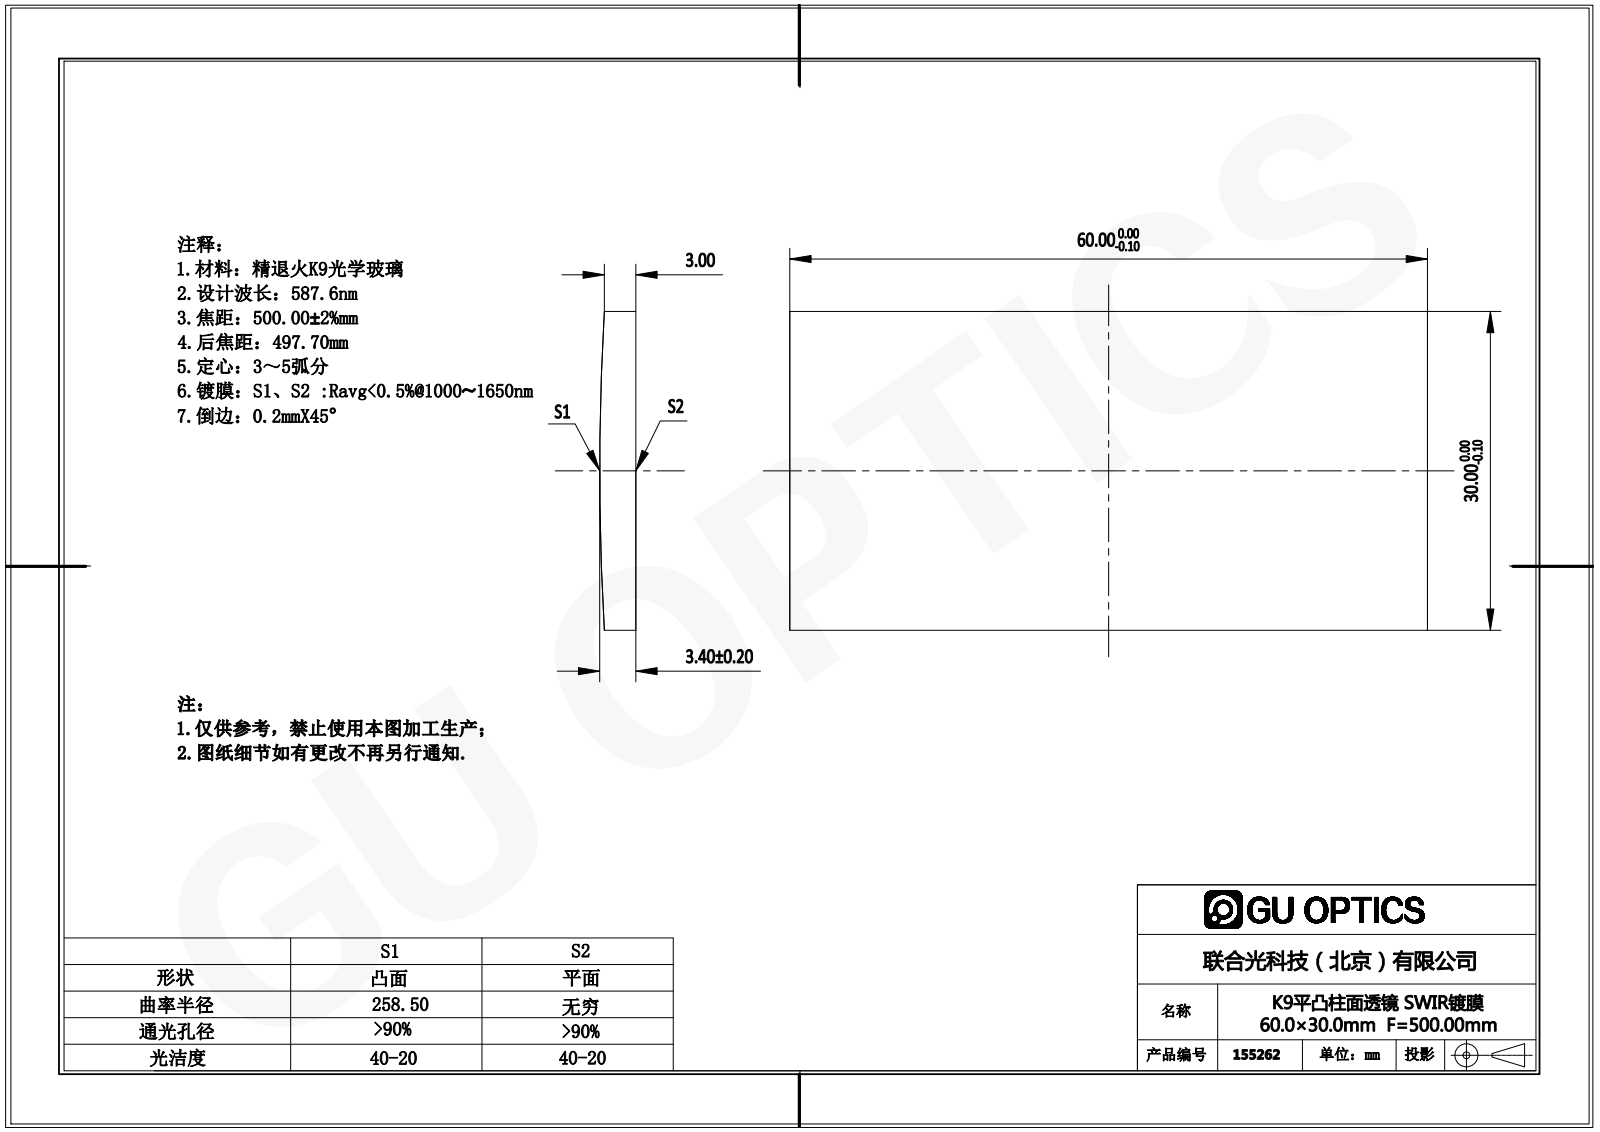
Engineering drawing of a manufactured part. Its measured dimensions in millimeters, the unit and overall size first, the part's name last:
Units: millimetres
Overall size (bounding box): 60 × 30 × 3.4
Partial cylindrical surfaces — rounded edges, fillets, slot ends (radius × count): R258.5 ×1
Main face-to-face distances: 30, 60
Volume: 5 859 mm³ · Surface area: 4 152 mm²
Bodies: 1 solid, 6 faces (5 planar, 1 cylindrical, 0 other)
Part name (STEP PRODUCT): 155064
STEP written by: SolidWorks 2016 (AUTOMOTIVE_DESIGN)
